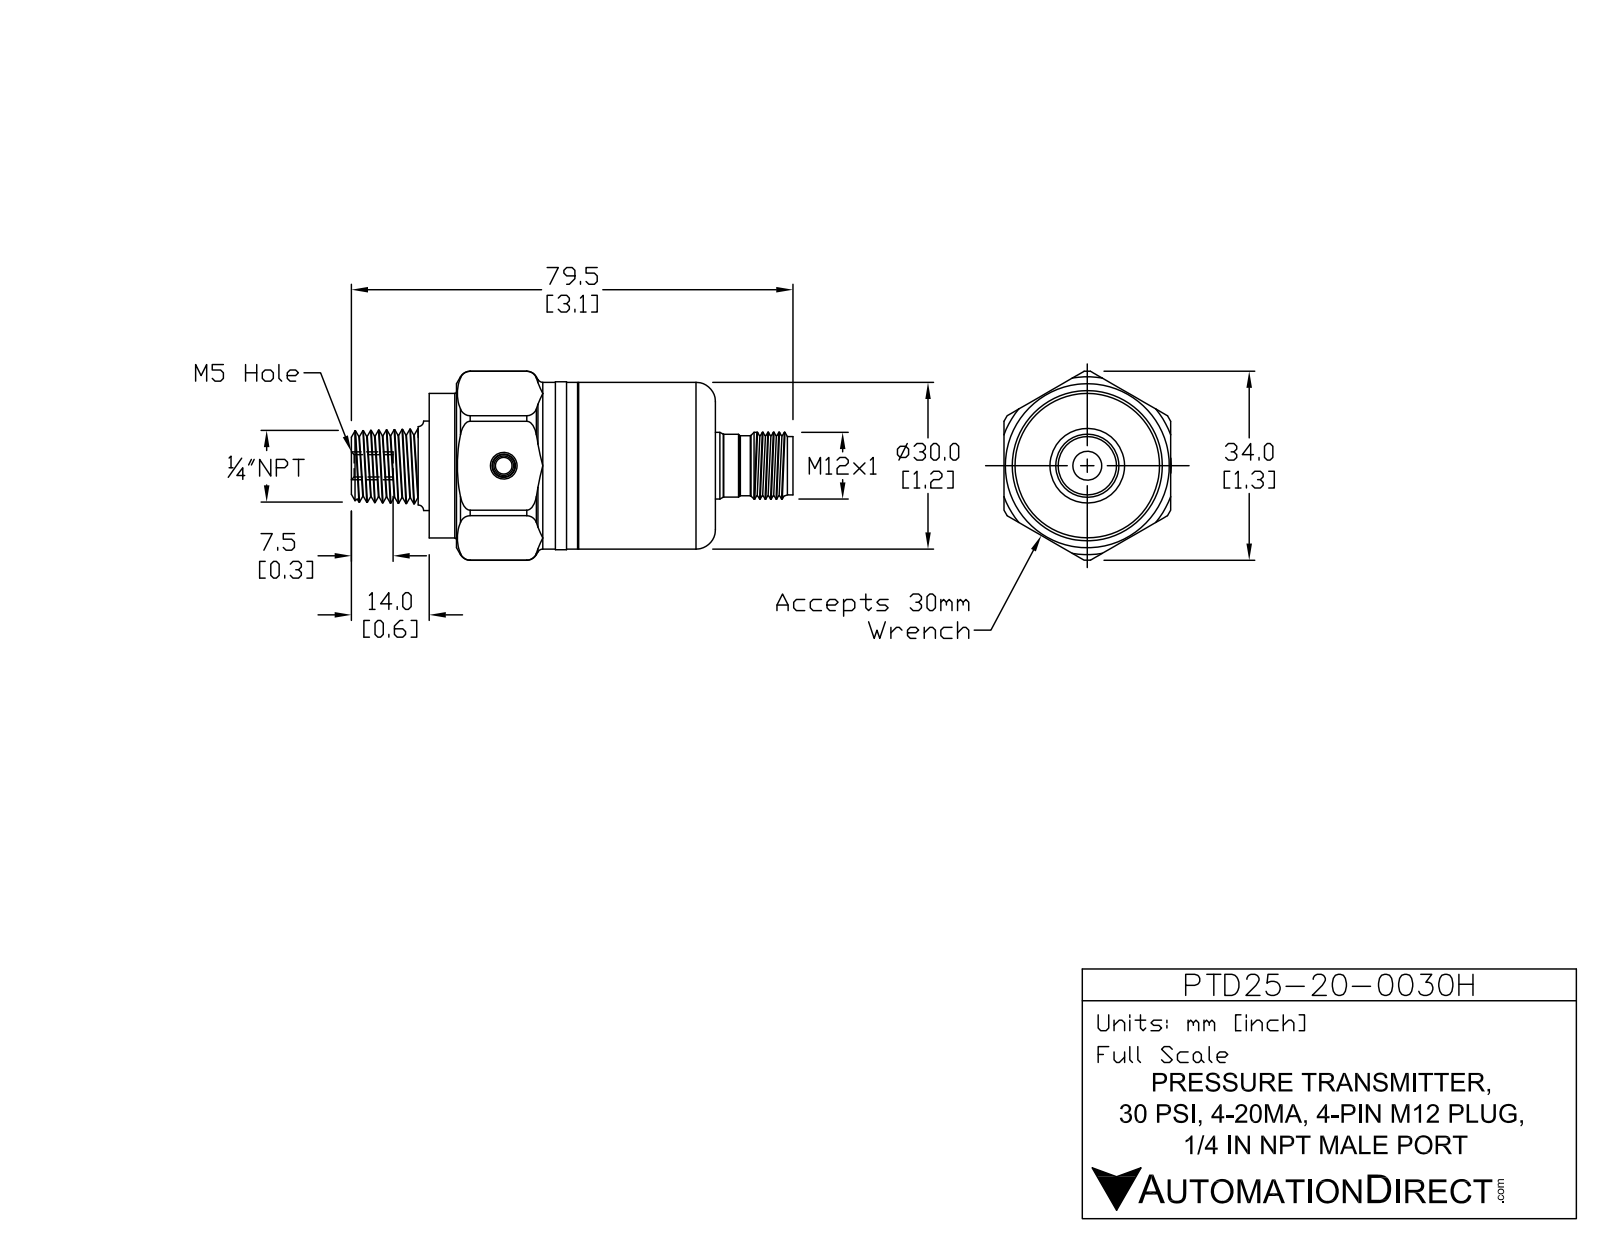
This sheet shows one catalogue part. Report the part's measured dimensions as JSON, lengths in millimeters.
{"part_name": "PTD25-20-0030H", "step_written_by": "SolidWorks 2017 (AUTOMOTIVE_DESIGN)", "units": "millimeters", "bodies": {"solids": 1, "faces": 124, "planar": 36, "cylindrical": 59, "other": 29}, "overall_size": [79.5, 33.78, 31.7], "volume_mm3": 39212, "surface_area_mm2": 8088, "round_holes": [[4, 1], [8.5, 1]], "round_bosses_or_shafts": [[30.05, 1], [30, 1], [25.96, 1], [14, 1], [13.5, 1], [12, 1]], "partial_cylinders_radius": [[3.76, 1], [16.95, 1]], "face_to_face_distances": [51, 29.98, 30, 48, 3, 65, 17, 14, 30.01, 5.65]}
